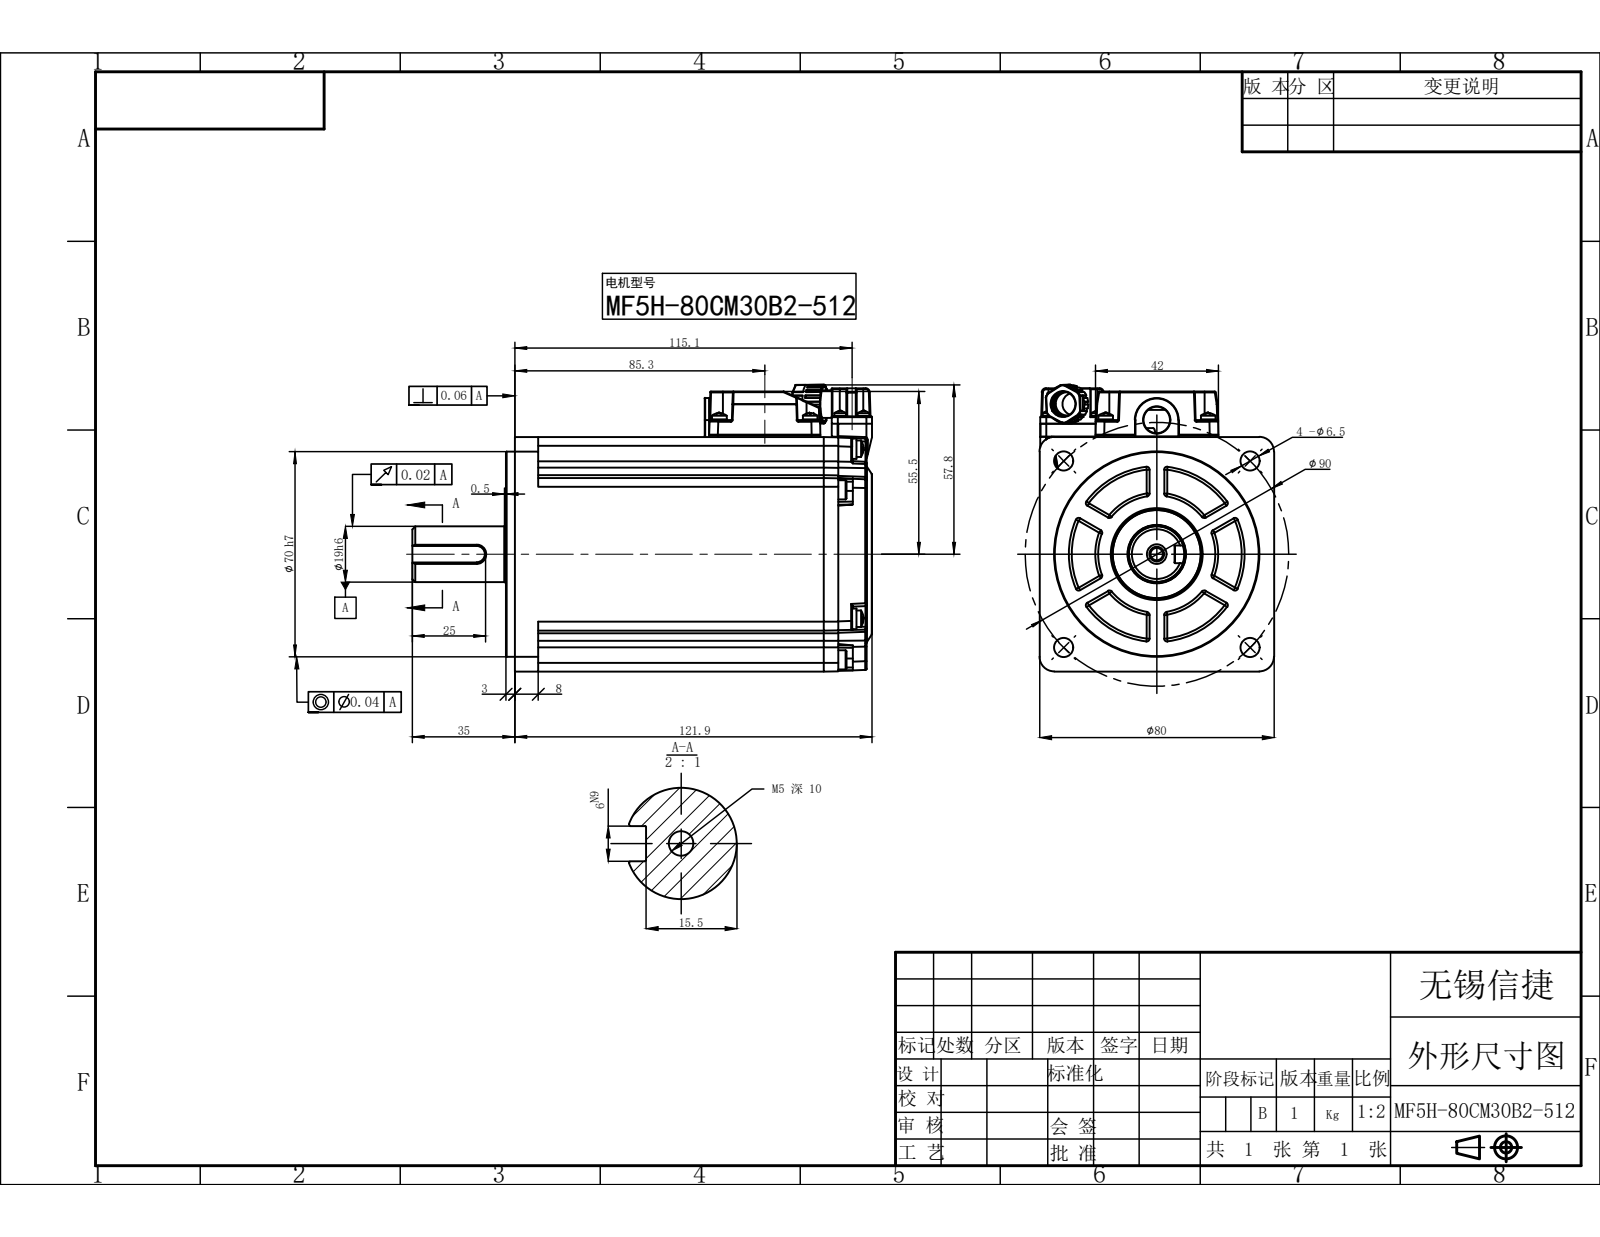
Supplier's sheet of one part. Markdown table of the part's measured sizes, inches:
| quantity | value |
| --- | --- |
| part name | MF5H-80CM30B2-512 |
| STEP written by | SolidWorks 2022 (CONFIG_CONTROL_DESIGN) |
| units | inches |
| bodies | 0 solids, 1062 faces (380 planar, 389 cylindrical, 293 other) |
| overall size | 6.177 × 3.853 × 3.15 |
| round holes (diameter × count) | 0.256 × 4, 0.165 × 1, 0.354 × 1, 0.409 × 1, 0.461 × 1, 0.787 × 1 |
| round bosses / shafts (diameter × count) | 0.276 × 4, 0.257 × 4, 0.22 × 4, 0.205 × 4, 0.197 × 4, 0.157 × 4, 2.756 × 1, 1.181 × 1 |
| partial cylindrical surfaces (radius × count) | 0.012 × 69, 0.039 × 39, 0.118 × 38, 0.02 × 31, 0.014 × 17, 0.008 × 13, 0.079 × 8, 0.01 × 4 |
| main face-to-face distances | 3.15, 0.551, 2.598, 4.799, 0.382, 0.071, 4.728, 4.346, 0.453, 2.047 |
| hole center spacings | 1.772, 2.506, 1.369, 3.303, 3.543, 1.803 |
